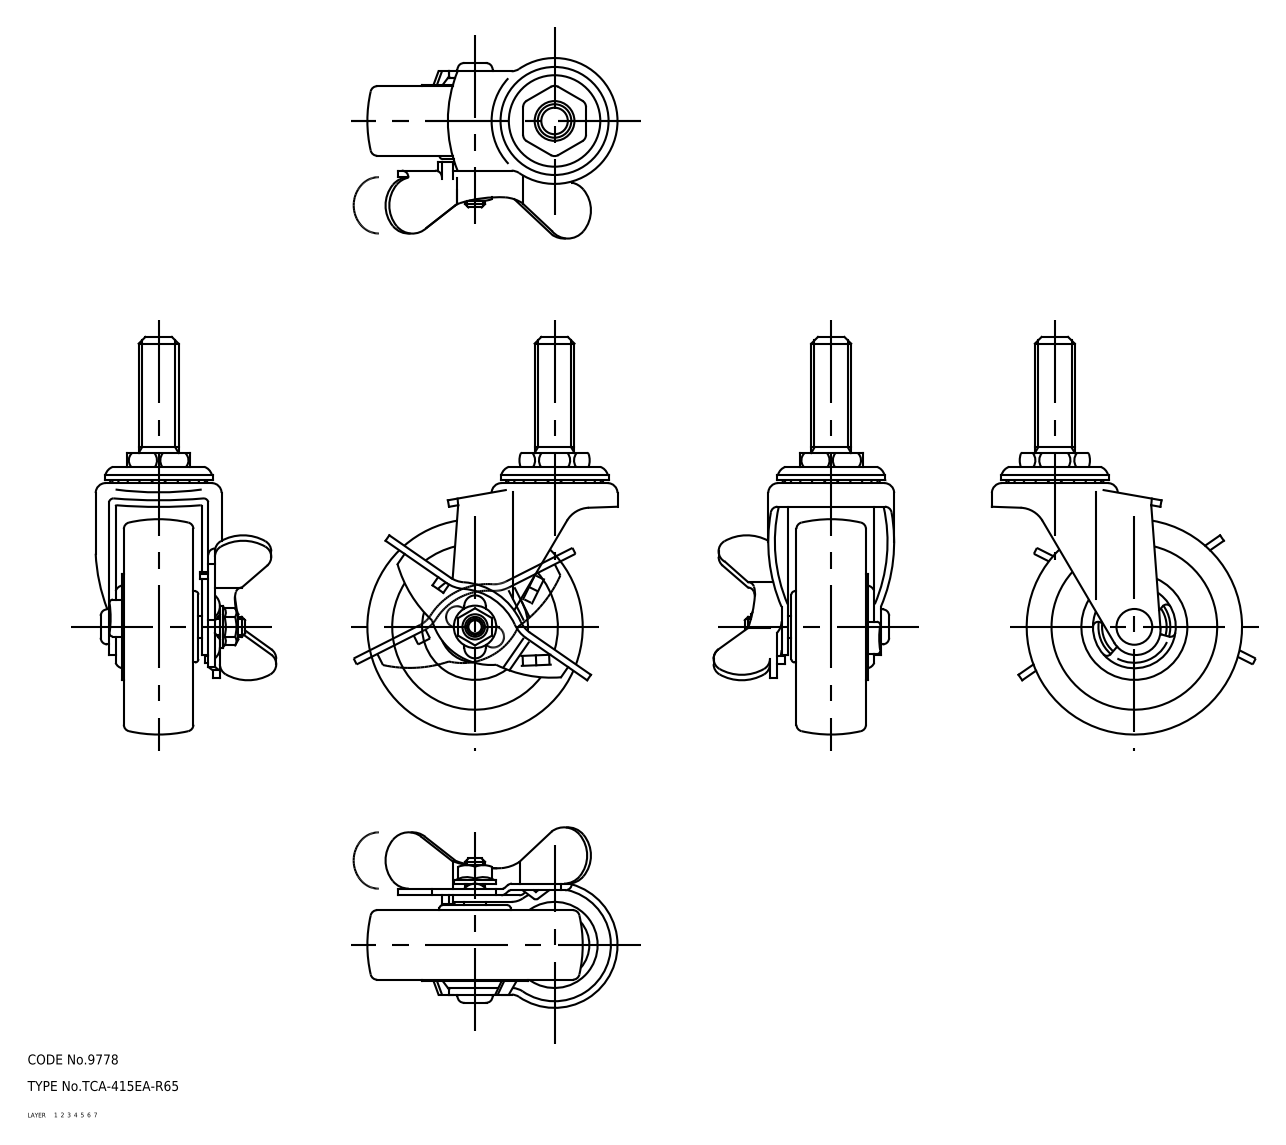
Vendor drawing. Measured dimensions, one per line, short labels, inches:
name: lever; wheel; mounting plate; main shaft (+2 more)
written by: CADfix (AUTOMOTIVE_DESIGN)
unit: in
bodies: 6 solids, 355 faces (0 planar, 0 cylindrical, 355 other)
size: 4.724 × 2.972 × 2.145
volume: 5.538 in³; area: 49.01 in²
